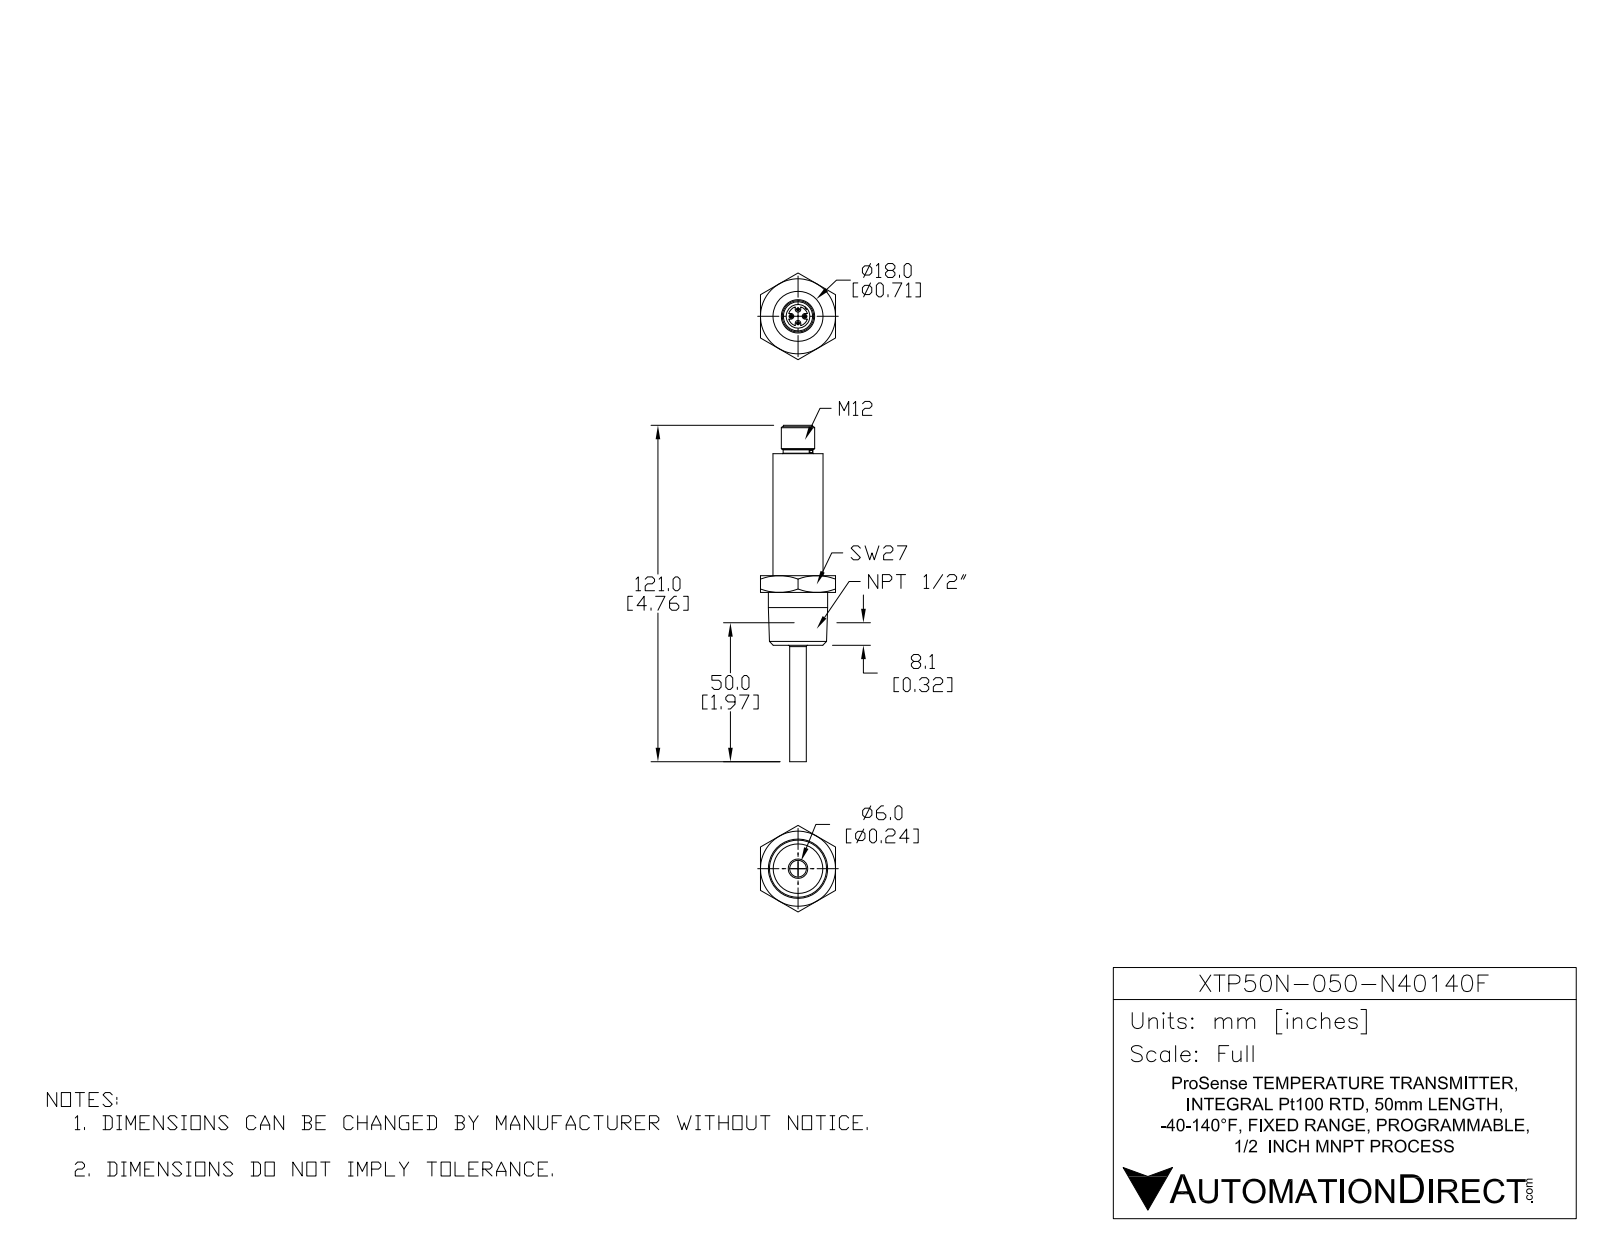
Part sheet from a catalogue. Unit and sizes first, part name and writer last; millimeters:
Units: millimetres
Overall size (bounding box): 121 × 31.18 × 27
Round holes (diameter × count): ⌀4 ×1, ⌀8.5 ×1
Round bosses / shafts (diameter × count): ⌀1.02 ×4, ⌀21.34 ×1, ⌀18 ×1, ⌀12 ×1, ⌀10.7 ×1, ⌀10.5 ×1, ⌀6 ×1
Partial cylindrical surfaces — rounded edges, fillets, slot ends (radius × count): R1 ×4, R3.5 ×1, R4.25 ×1
Main face-to-face distances: 27, 25, 19, 6, 68.9, 49.9, 43.9, 79.1, 60.1, 54.1
Volume: 22 920 mm³ · Surface area: 7 274 mm²
Bodies: 1 solid, 117 faces (43 planar, 34 cylindrical, 40 other)
Part name (STEP PRODUCT): XTP50N-050-N40140F
STEP written by: SolidWorks 2015 (AUTOMOTIVE_DESIGN)
